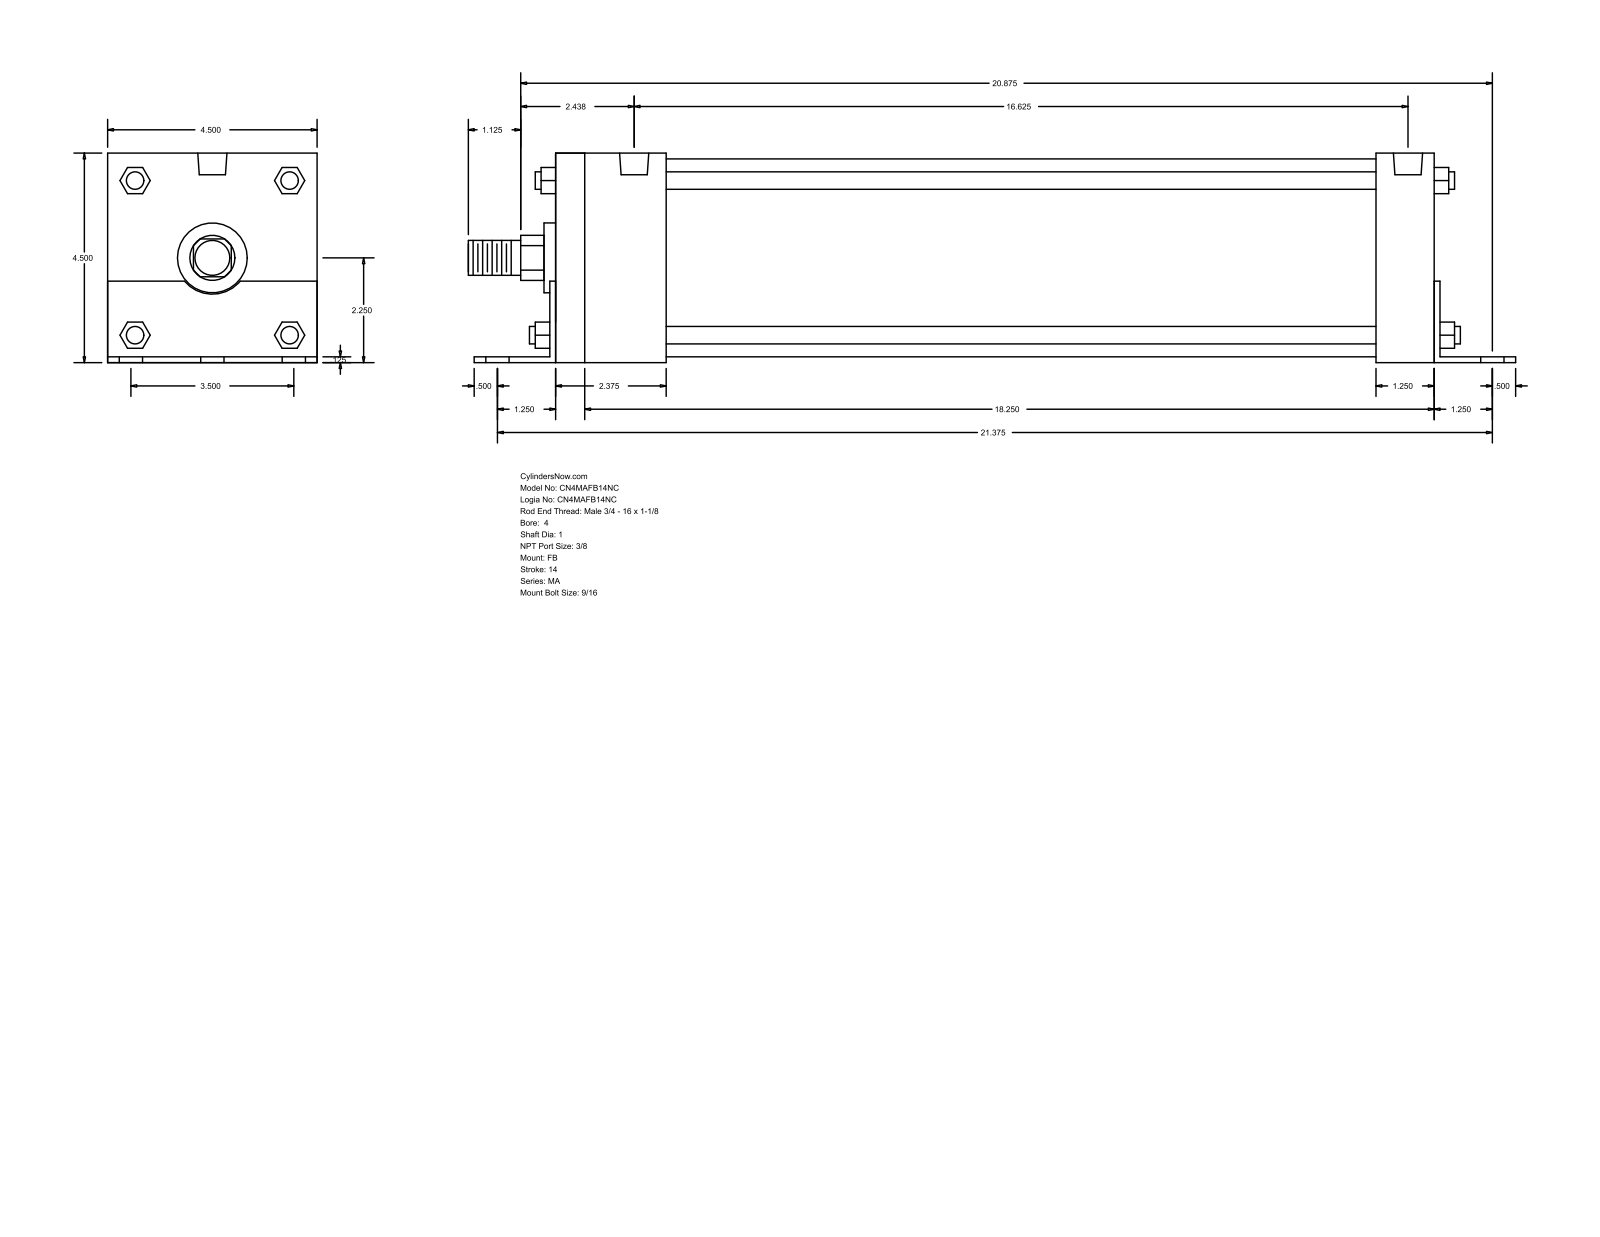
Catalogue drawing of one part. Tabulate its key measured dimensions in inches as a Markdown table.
| quantity | value |
| --- | --- |
| part name | MA_FB__0400_1 |
| STEP written by | GSSL Pune (CONFIG_CONTROL_DESIGN) |
| units | inches |
| bodies | 0 solids, 140 faces (105 planar, 35 cylindrical, 0 other) |
| overall size | 22.5 × 4.502 × 4.5 |
| round holes (diameter × count) | 0.563 × 6, 0.437 × 4, 0.627 × 2 |
| round bosses / shafts (diameter × count) | 0.375 × 4, 4.25 × 1, 1.5 × 1, 1 × 1, 0.75 × 1 |
| partial cylindrical surfaces (radius × count) | 0.484 × 1, 0.78 × 1 |
| main face-to-face distances | 4.5, 0.125, 4.502, 19, 0.123, 4.377, 18.875, 19.125, 17.75, 17.625 |
| hole center spacings | 1.75, 21.447, 21.375, 0.187, 2.52, 2.657, 3.419, 3.5 |
